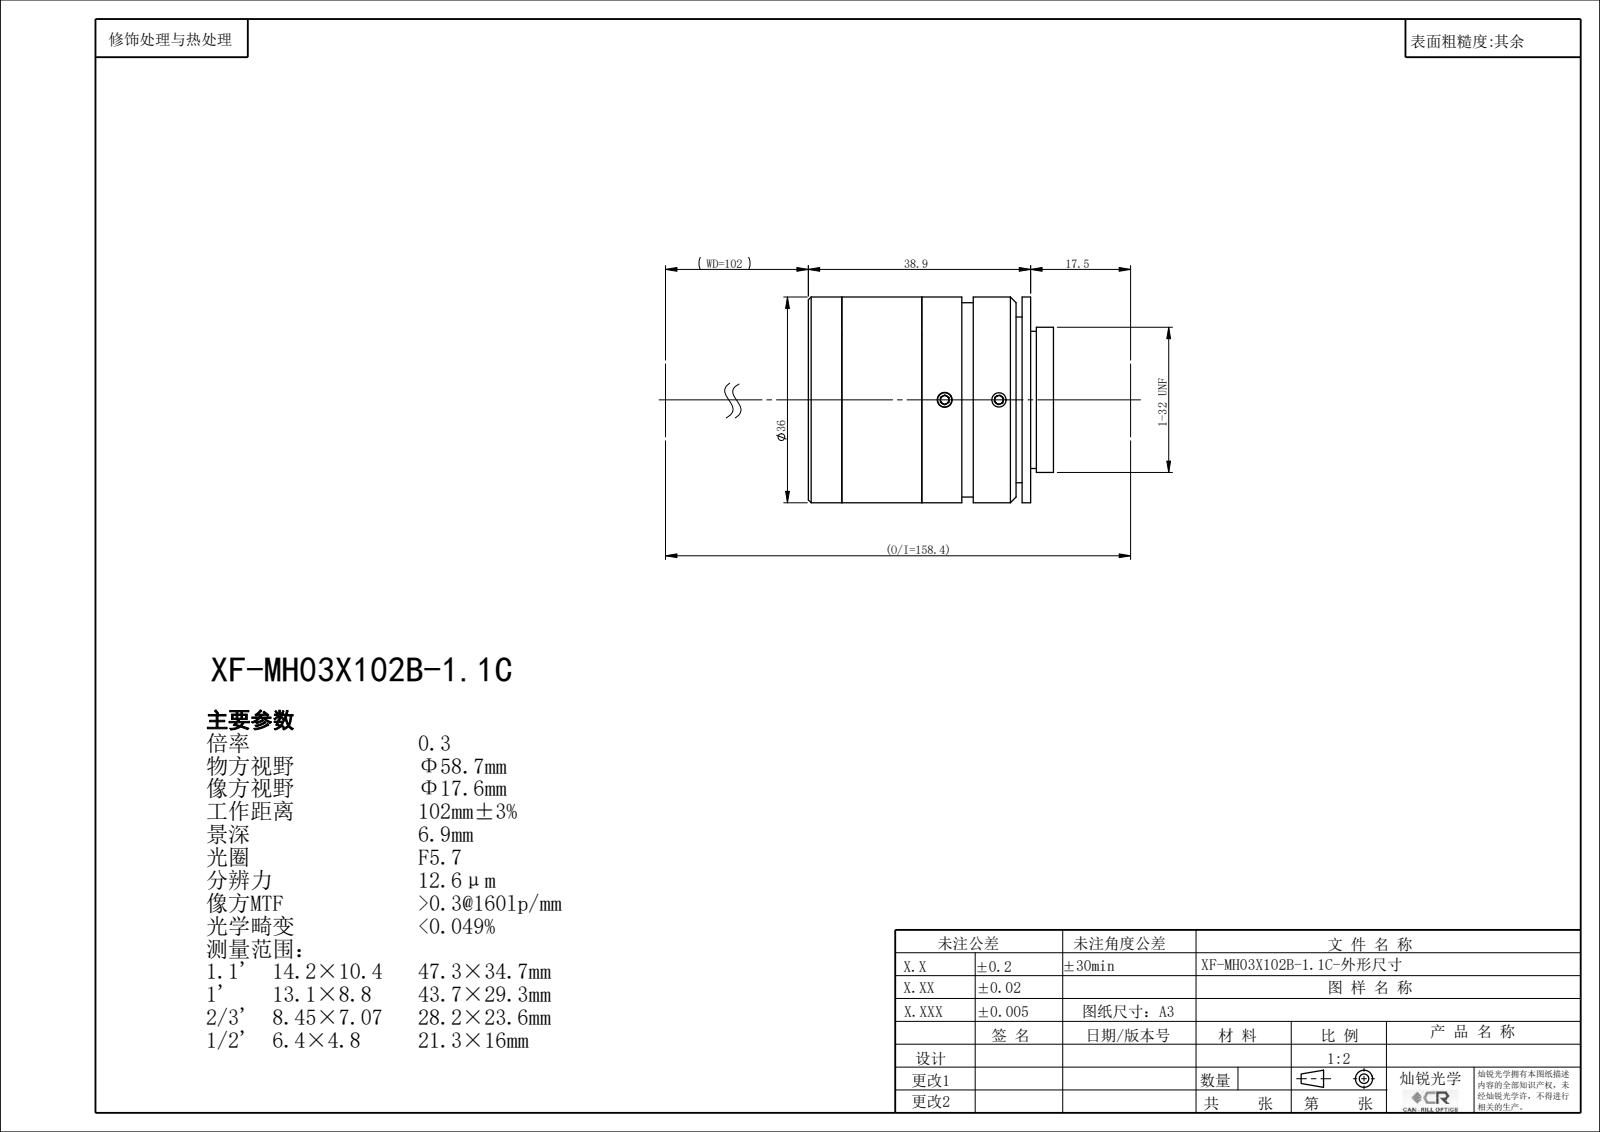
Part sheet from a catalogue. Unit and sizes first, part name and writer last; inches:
Units: inches
Overall size (bounding box): 1.69 × 1.417 × 1.417
Round holes (diameter × count): ⌀0.098 ×3, ⌀0.551 ×1, ⌀0.646 ×1, ⌀0.669 ×1, ⌀0.724 ×1, ⌀0.882 ×1, ⌀0.945 ×1, ⌀0.98 ×1, ⌀1.024 ×1
Round bosses / shafts (diameter × count): ⌀1.417 ×1, ⌀1.339 ×1, ⌀1 ×1
Main face-to-face distances: 0.75, 0.783, 1.532, 0.059, 1.473, 0.691, 0.231, 0.551, 1.242, 1.301
Bodies: 0 solids, 144 faces (72 planar, 38 cylindrical, 34 other)
Part name (STEP PRODUCT): XF-MH03X102B-1.1C
STEP written by: SolidWorks 2022 (CONFIG_CONTROL_DESIGN)
